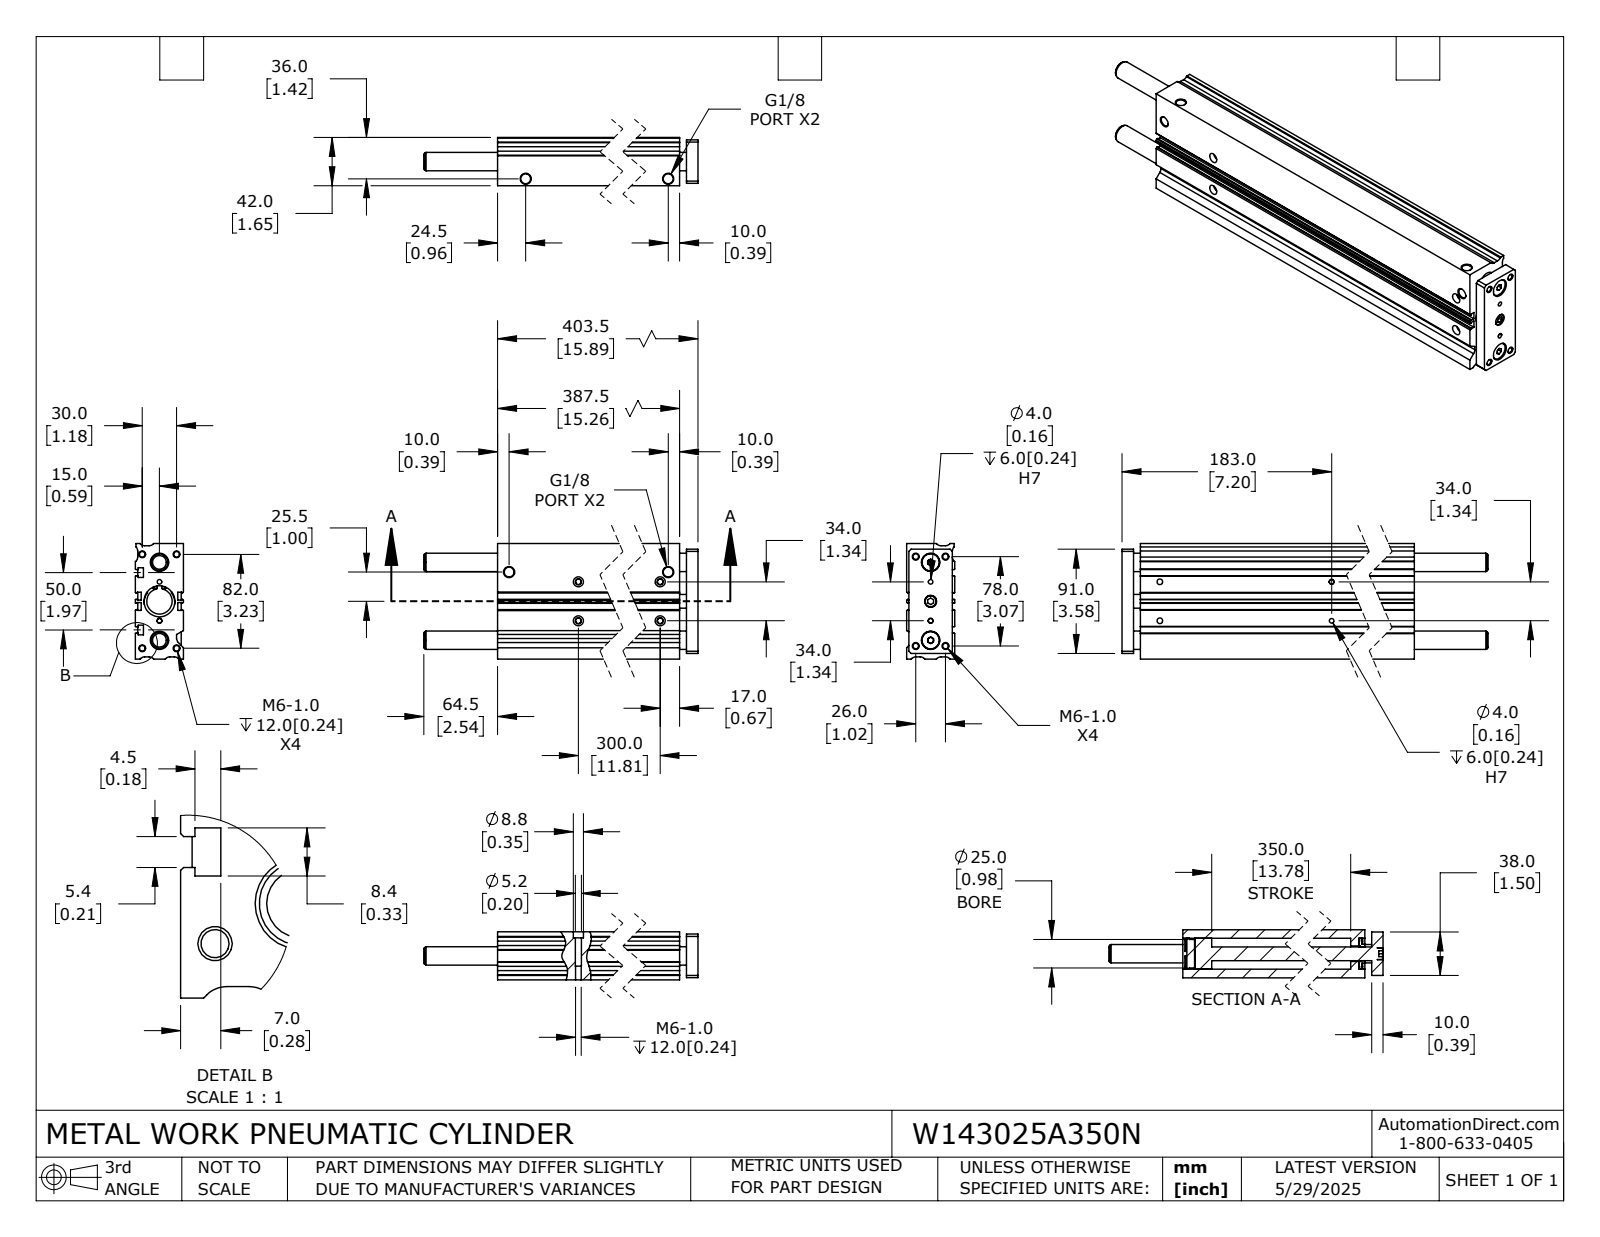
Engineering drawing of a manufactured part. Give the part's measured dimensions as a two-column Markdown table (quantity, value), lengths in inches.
| quantity | value |
| --- | --- |
| part name | W143025A350N_ROD; W143025A350N; W143025A350N_BODY |
| STEP written by | SolidWorks 2024 (CONFIG_CONTROL_DESIGN) |
| units | inches |
| bodies | 6 solids, 390 faces (191 planar, 157 cylindrical, 42 other) |
| overall size | 18.425 × 3.976 × 1.654 |
| volume | 84.82 in³ |
| surface area | 478.7 in² |
| round holes (diameter × count) | 0.194 × 6, 0.194 × 6, 0.067 × 4, 0.157 × 4, 0.205 × 4, 0.337 × 4, 0.346 × 4, 0.63 × 2, 0.413 × 1, 0.472 × 1, 0.539 × 1, 0.874 × 1 |
| round bosses / shafts (diameter × count) | 0.61 × 2, 1.063 × 1, 0.984 × 1, 0.65 × 1, 0.394 × 1 |
| partial cylindrical surfaces (radius × count) | 0.039 × 12, 0.197 × 9, 0.079 × 8, 0.524 × 2, 0.559 × 1 |
| main face-to-face distances | 1.654, 0.079, 0.197, 1.457, 1.378, 3.976, 0.839, 2.299, 0.276, 0.354 |
| hole center spacings | 1.339, 0.111, 0.29, 0.5, 0.548, 0.652, 0.669, 0.902 |
